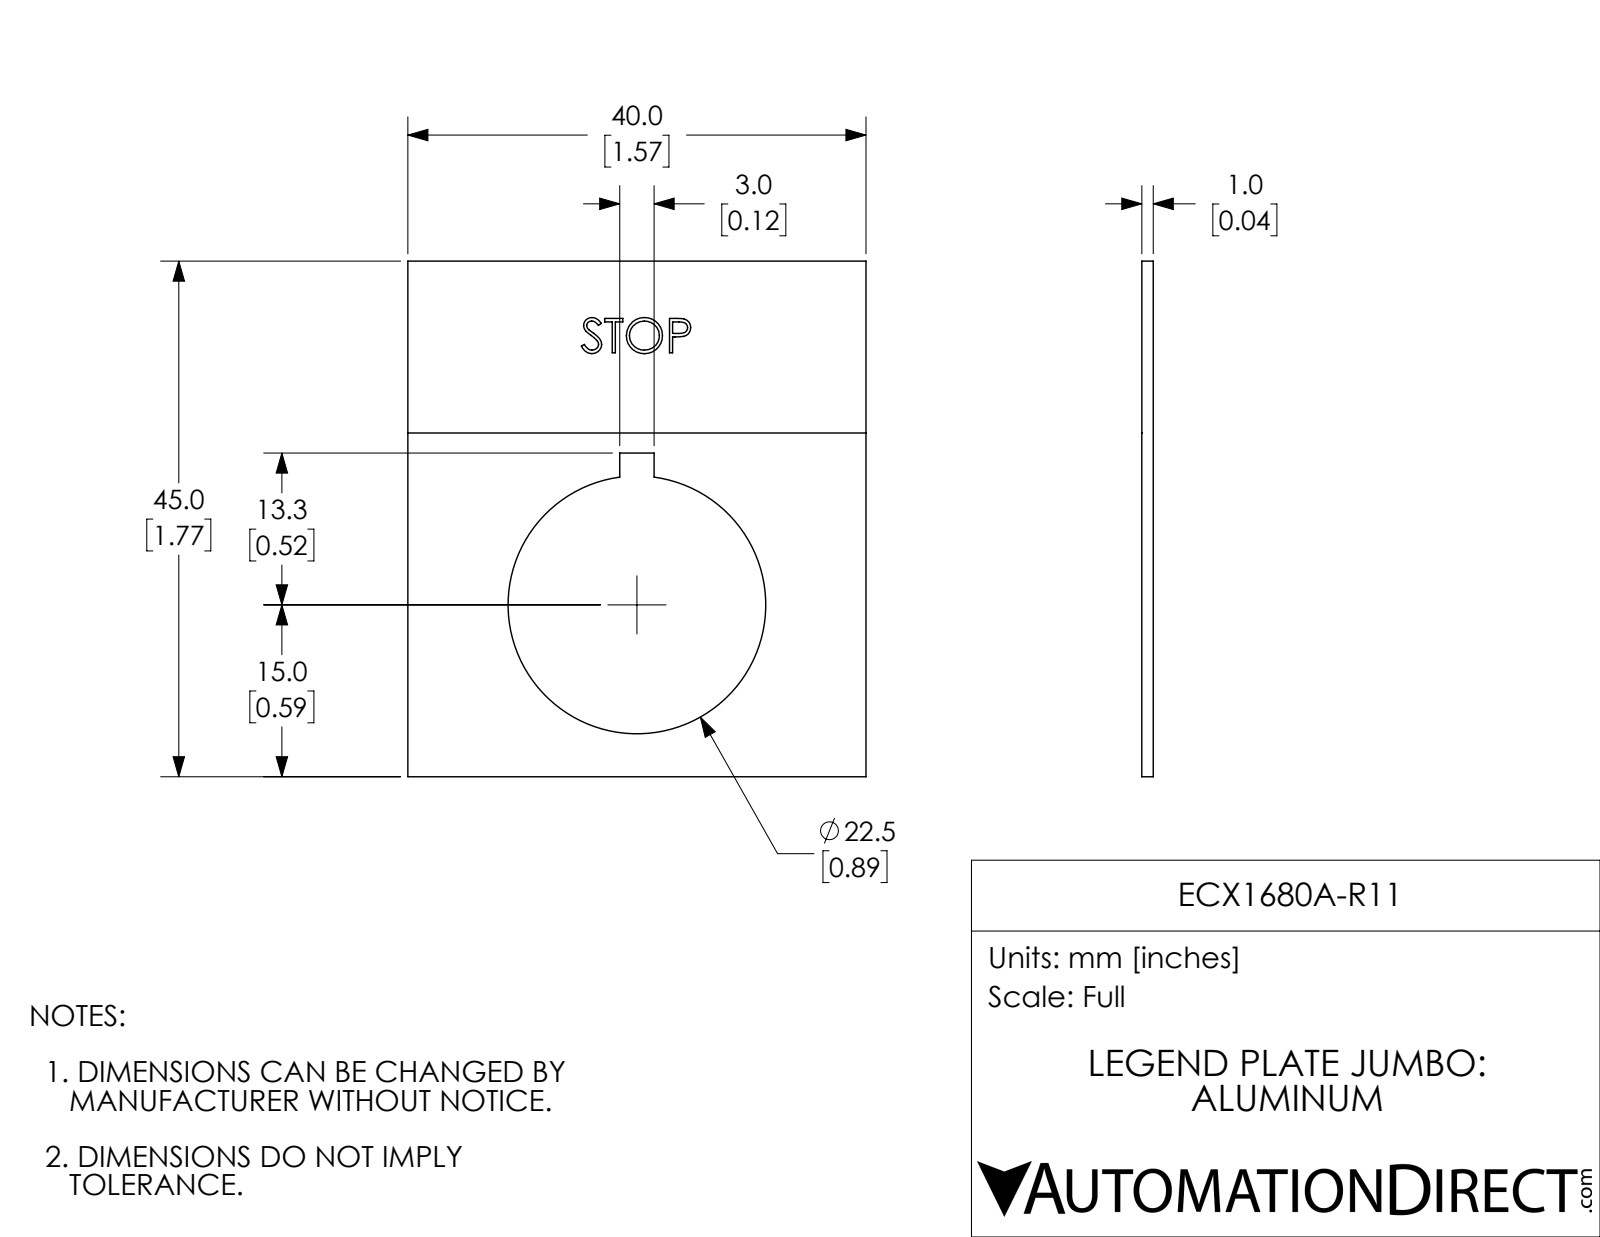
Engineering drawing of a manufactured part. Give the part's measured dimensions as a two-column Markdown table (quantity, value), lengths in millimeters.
| quantity | value |
| --- | --- |
| part name | ECX1680A-R11 |
| STEP written by | SolidWorks 2017 (AUTOMOTIVE_DESIGN) |
| units | millimeters |
| bodies | 1 solid, 67 faces (35 planar, 3 cylindrical, 29 other) |
| overall size | 45 × 40 × 1 |
| volume | 1 393 mm³ |
| surface area | 3 038 mm² |
| round holes (diameter × count) | 22.5 × 1 |
| main face-to-face distances | 1, 0.99, 40, 45, 18.5, 21.5, 28.25, 16.75, 3, 30 |
